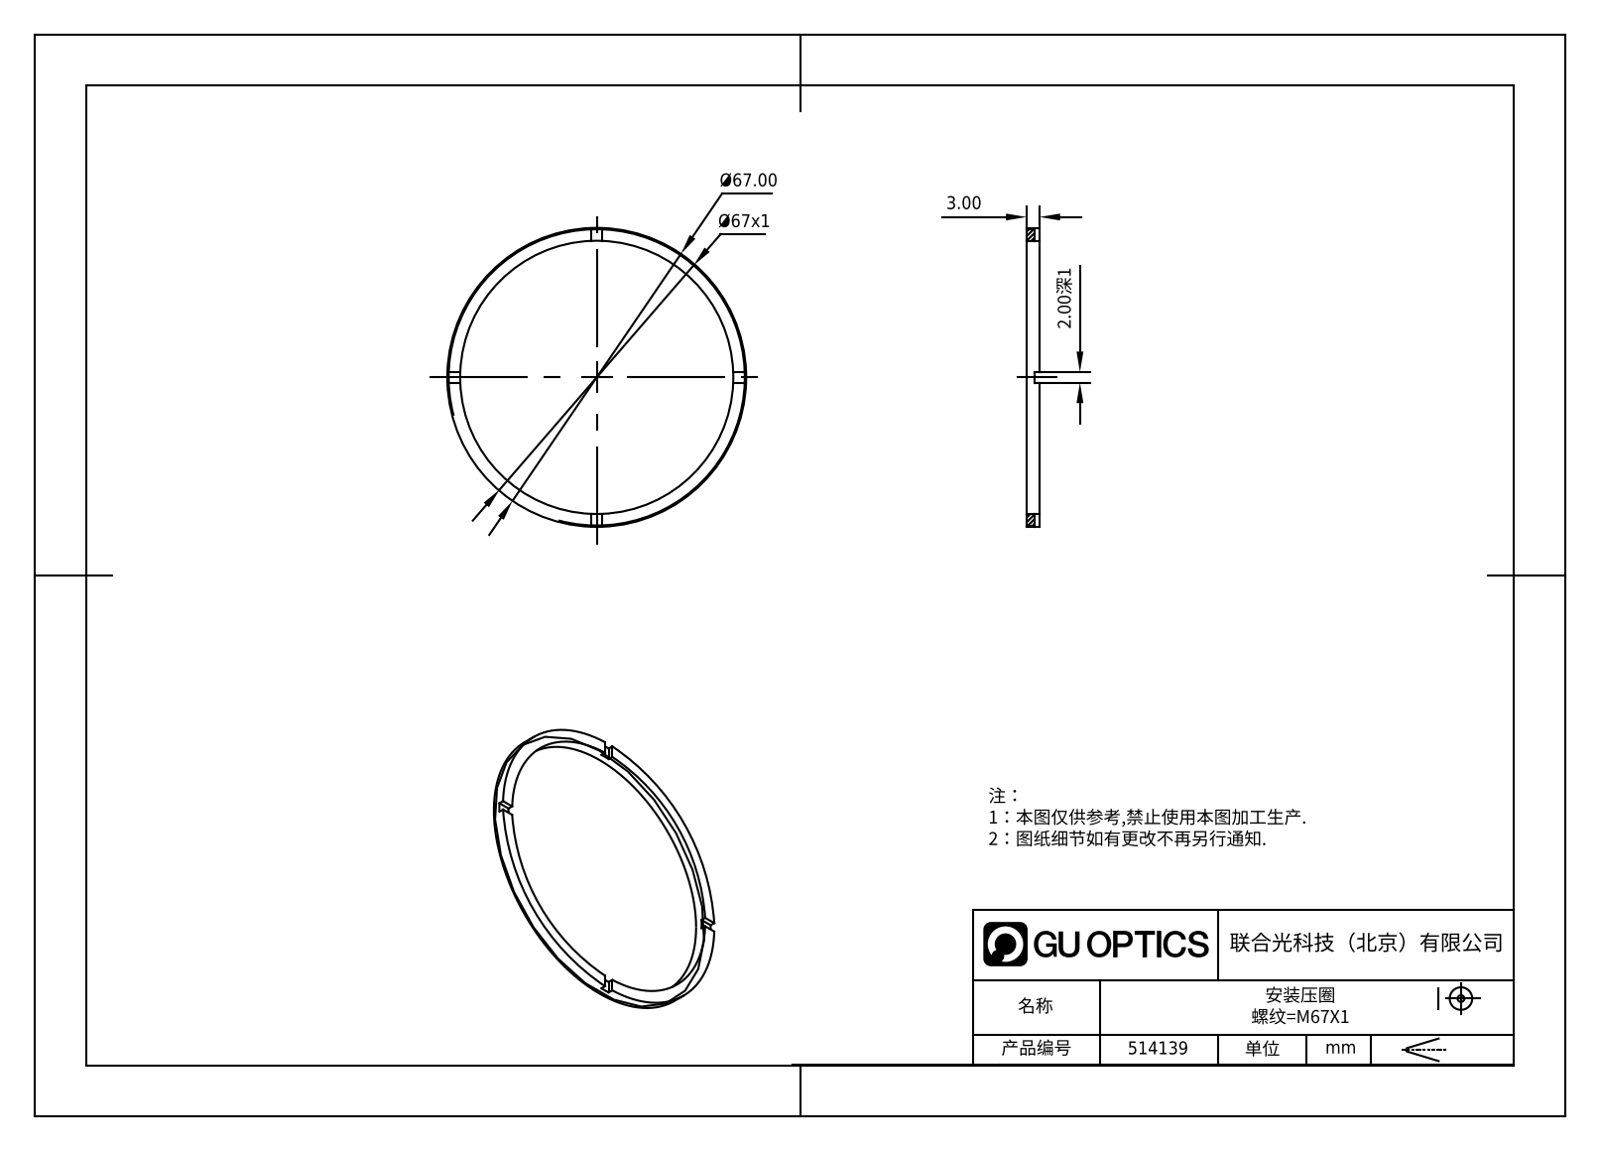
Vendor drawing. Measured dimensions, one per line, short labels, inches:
name: 514139
written by: SolidWorks 2020 (CONFIG_CONTROL_DESIGN)
unit: in
bodies: 1 solid, 21 faces (17 planar, 4 cylindrical, 0 other)
size: 2.638 × 2.638 × 0.118
volume: 0.092 in³; area: 3.461 in²
holes: 1× ⌀2.441
bosses: 1× ⌀2.638
face distances: 0.118, 0.079, 0.039
